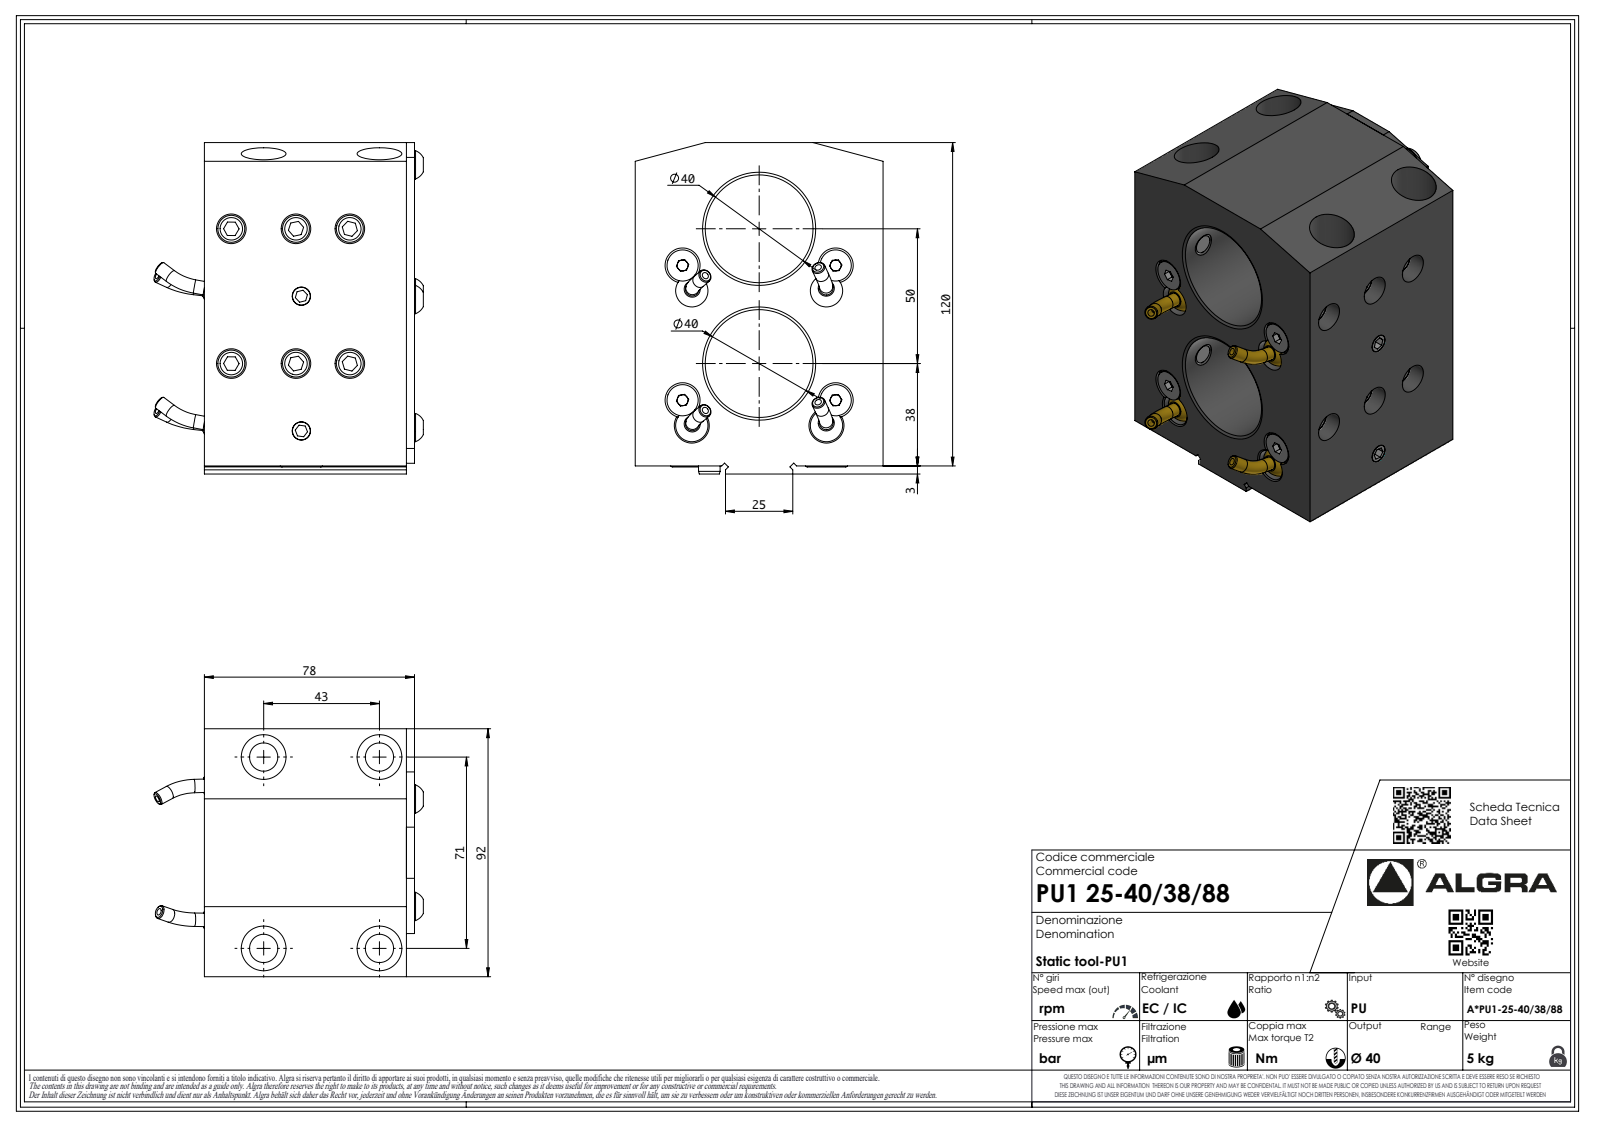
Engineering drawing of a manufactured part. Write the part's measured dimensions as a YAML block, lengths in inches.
part_name: "PU125-403888"
step_written_by: "SolidWorks 2023 (AUTOMOTIVE_DESIGN)"
units: inches
bodies: {solids: 1, faces: 366, planar: 208, cylindrical: 37, other: 121}
overall_size: [4.843, 3.807, 3.622]
volume: 39.89
surface_area: 116.1
round_holes:
  - {diameter: 1.575, count: 2}
  - {diameter: 0.083, count: 1}
round_bosses_or_shafts:
  - {diameter: 0.197, count: 8}
  - {diameter: 0.315, count: 1}
  - {diameter: 0.251, count: 1}
  - {diameter: 0.067, count: 1}
partial_cylinders:
  - {radius: 0.013, count: 7}
  - {radius: 0.02, count: 7}
  - {radius: 0.146, count: 7}
  - {radius: 0.008, count: 1}
face_to_face_distances: [0.118, 3.622, 3.071, 2.953, 4.724, 4.843, 0.63, 2.992, 2.362, 1.319]
hole_center_spacings: [1.969]
